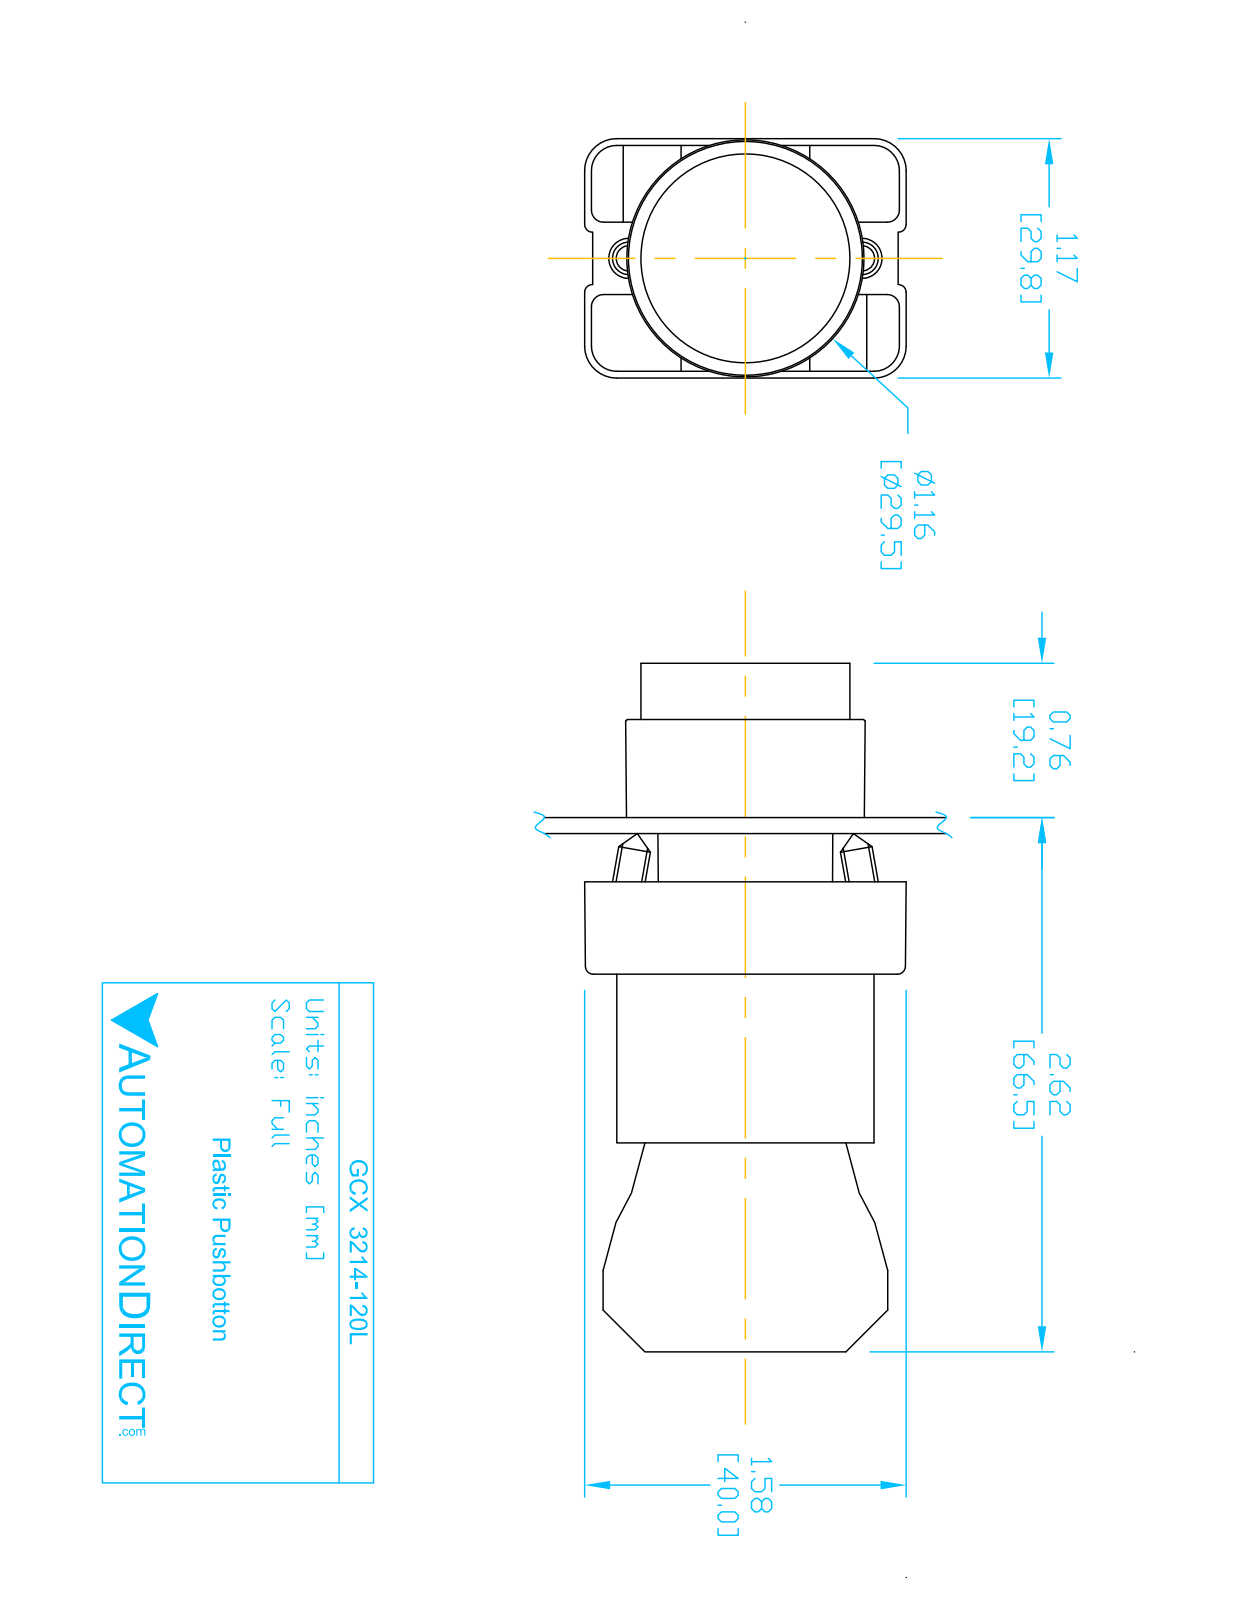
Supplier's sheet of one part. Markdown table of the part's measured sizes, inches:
| quantity | value |
| --- | --- |
| part name | ecx1040; GCX3214L OPERATOR; ECX3029-2; GCX3214-120L (+1 more) |
| STEP written by | SolidWorks 2016 (AUTOMOTIVE_DESIGN) |
| units | inches |
| bodies | 7 solids, 425 faces (250 planar, 144 cylindrical, 31 other) |
| overall size | 3.319 × 1.581 × 1.177 |
| volume | 2.721 in³ |
| surface area | 36.32 in² |
| round holes (diameter × count) | 0.079 × 2, 0.124 × 2, 0.13 × 2, 0.087 × 1, 0.197 × 1, 0.469 × 1, 0.878 × 1, 0.888 × 1, 1.024 × 1 |
| round bosses / shafts (diameter × count) | 0.157 × 4, 1.175 × 1, 1.004 × 1, 0.945 × 1, 0.856 × 1, 0.78 × 1, 0.504 × 1 |
| partial cylindrical surfaces (radius × count) | 0.059 × 24, 0.041 × 12, 0.124 × 12, 0.157 × 12, 0.039 × 8, 0.128 × 2, 0.02 × 1, 0.063 × 1 |
| main face-to-face distances | 0.827, 0.579, 1.171, 2.02, 1.193, 0.031, 0.033, 0.573, 1.165, 0.593 |
| hole center spacings | 0.236, 0.544, 0.472, 0.49 |
